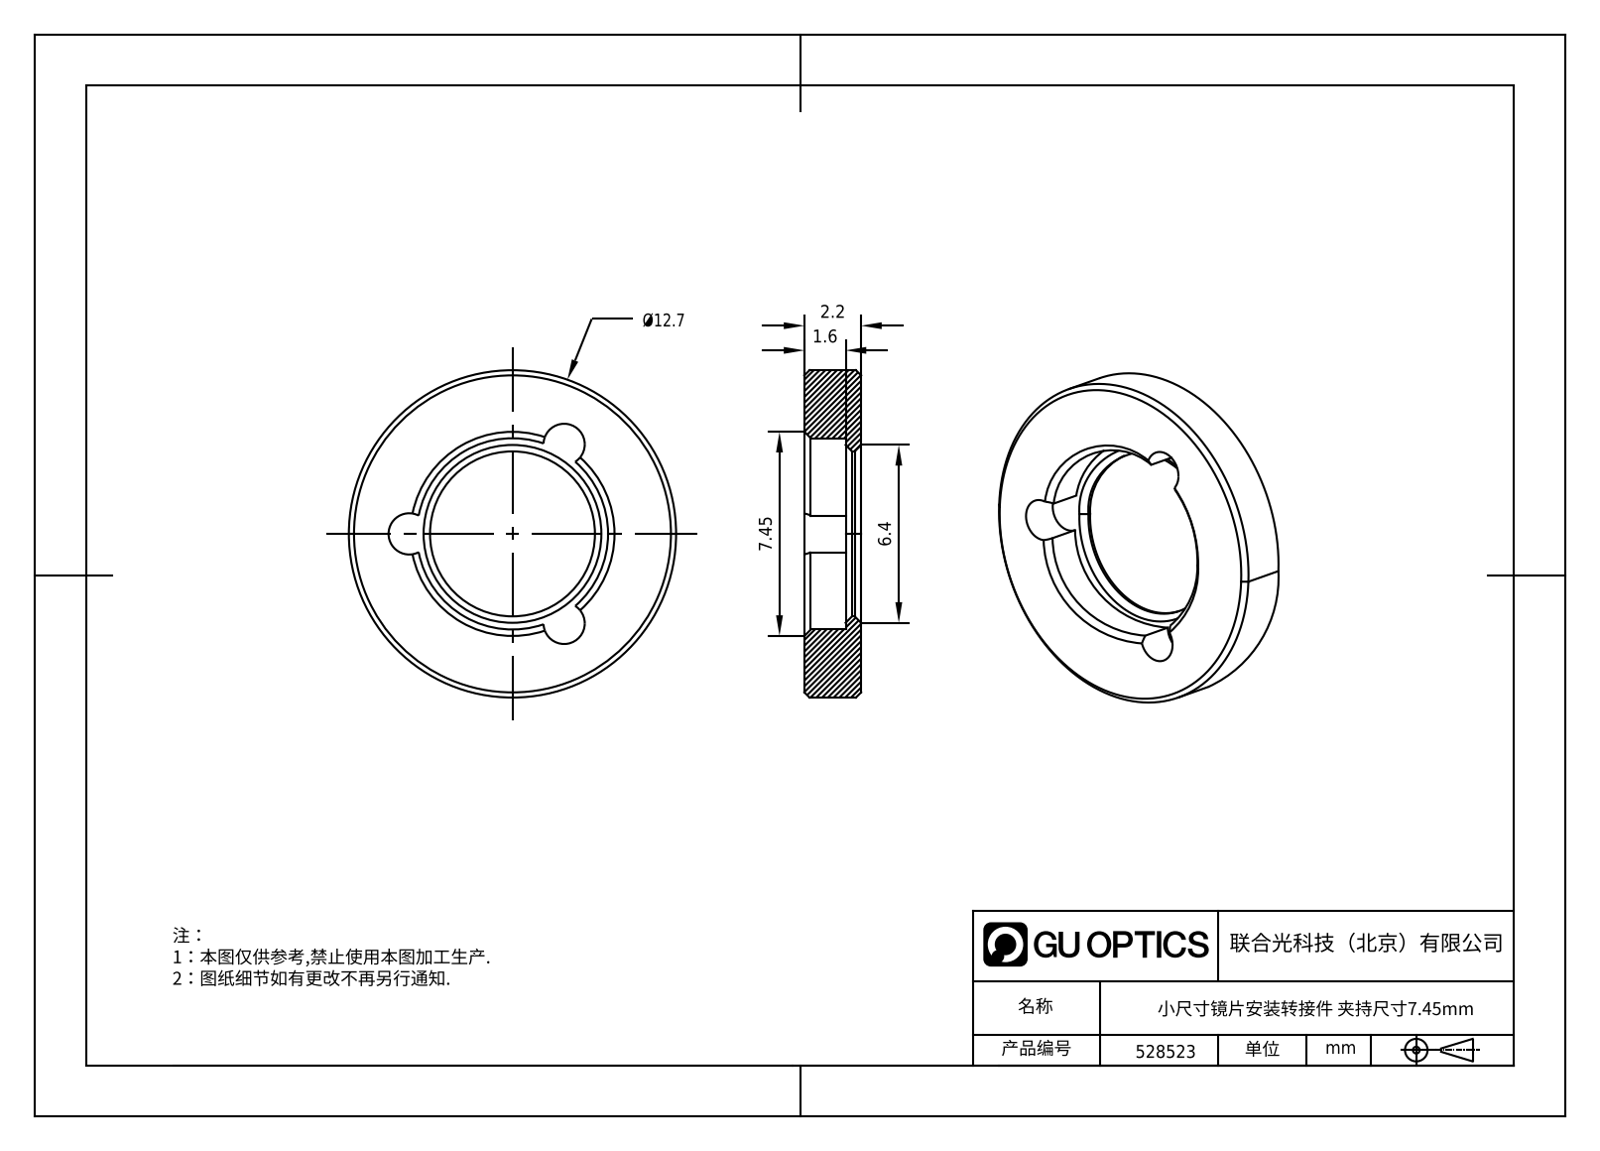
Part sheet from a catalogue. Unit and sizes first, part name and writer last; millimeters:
Units: millimetres
Overall size (bounding box): 12.7 × 12.7 × 2.2
Round holes (diameter × count): ⌀6.4 ×1, ⌀7.42 ×1
Round bosses / shafts (diameter × count): ⌀12.7 ×1
Partial cylindrical surfaces — rounded edges, fillets, slot ends (radius × count): R0.8 ×3
Main face-to-face distances: 2.2, 0.6, 1.6
Volume: 179 mm³ · Surface area: 317 mm²
Bodies: 1 solid, 28 faces (3 planar, 13 cylindrical, 12 other)
Part name (STEP PRODUCT): 1.6.4.9-ZSJ-05-7.4
STEP written by: SolidWorks 2021 (CONFIG_CONTROL_DESIGN)
